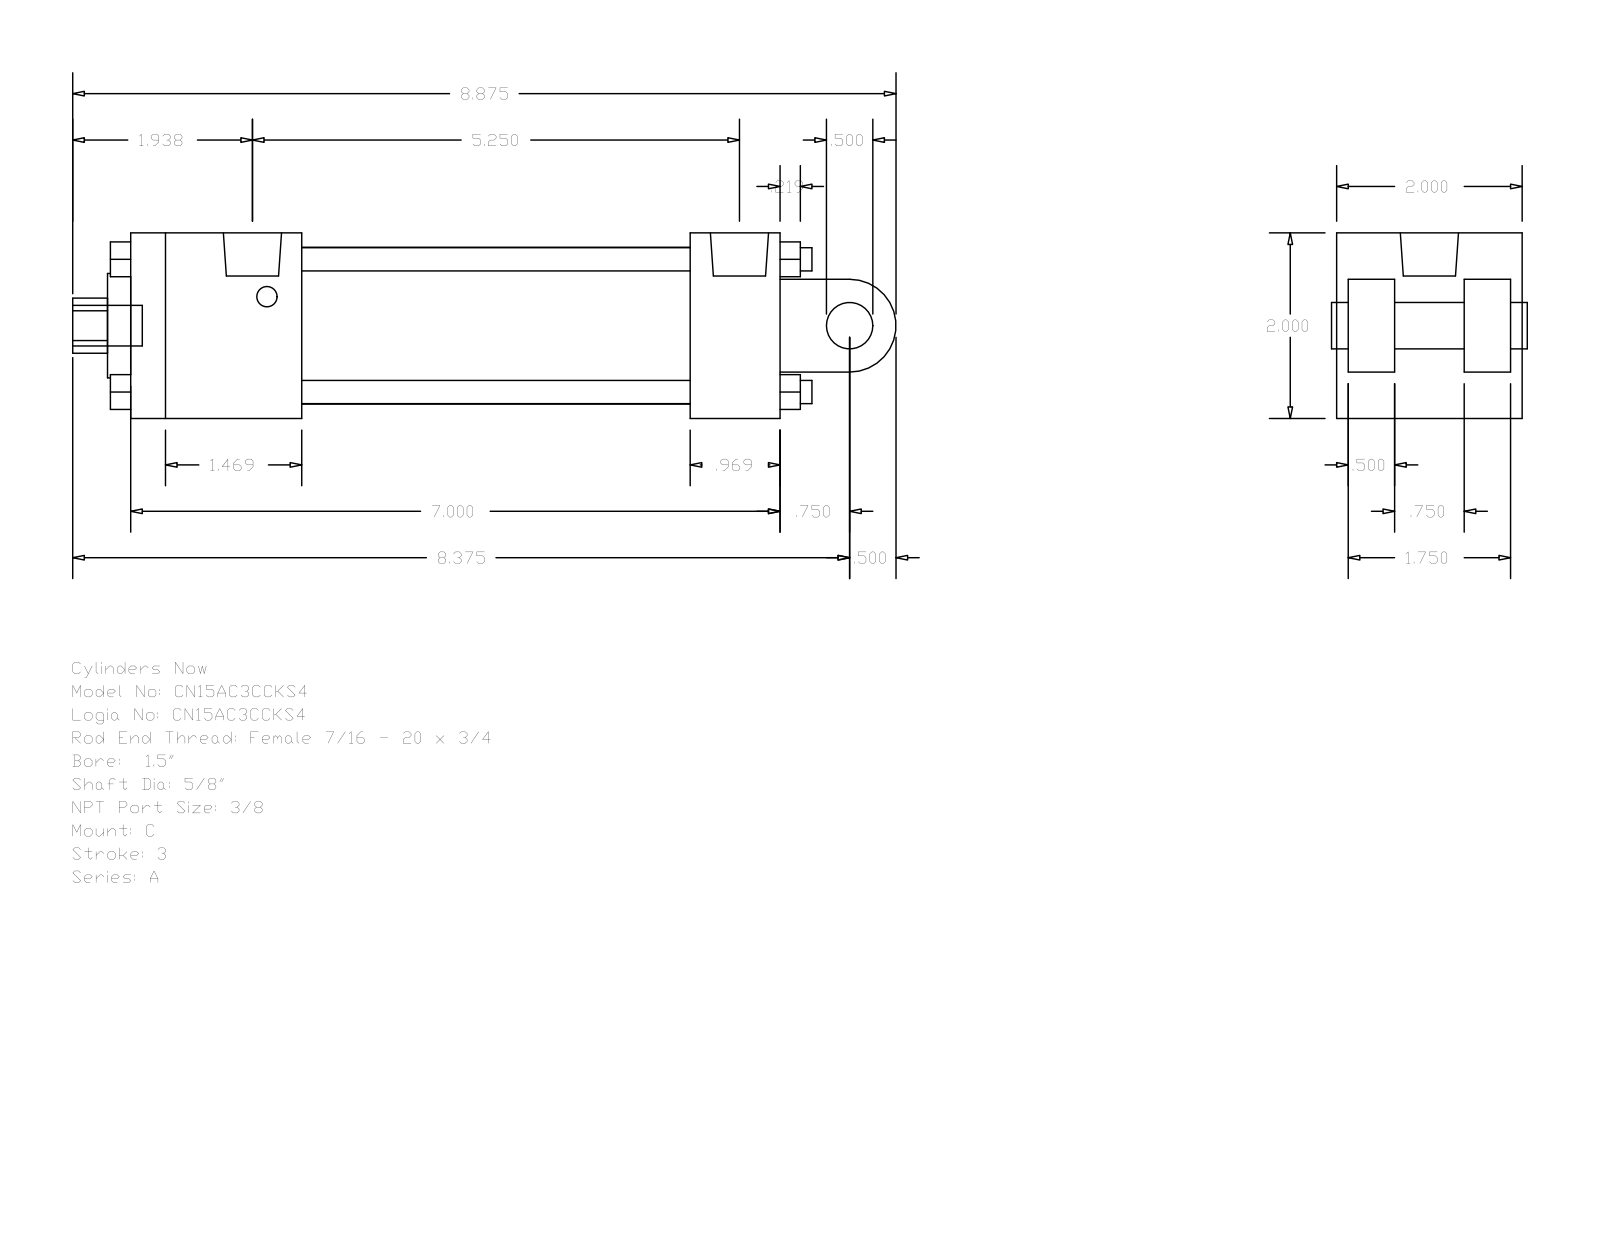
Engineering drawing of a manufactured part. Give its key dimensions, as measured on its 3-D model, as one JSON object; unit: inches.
{"part_name": "A_C__0150_0.625", "step_written_by": "GSSL Pune (CONFIG_CONTROL_DESIGN)", "units": "inches", "bodies": {"solids": 0, "faces": 135, "planar": 102, "cylindrical": 33, "other": 0}, "overall_size": [8.875, 2, 2], "round_holes": [[0.219, 2], [0.625, 1], [0.627, 1], [1.125, 1], [1.69, 1]], "round_bosses_or_shafts": [[0.25, 4], [0.219, 2], [0.627, 1], [0.5, 1], [0.437, 1]], "partial_cylinders_radius": [[0.297, 1], [0.5, 1]], "face_to_face_distances": [2, 0.5, 7, 0.125, 1.875, 0.625, 1.375, 1.25, 6.031, 0.969], "hole_center_spacings": [0.156]}
